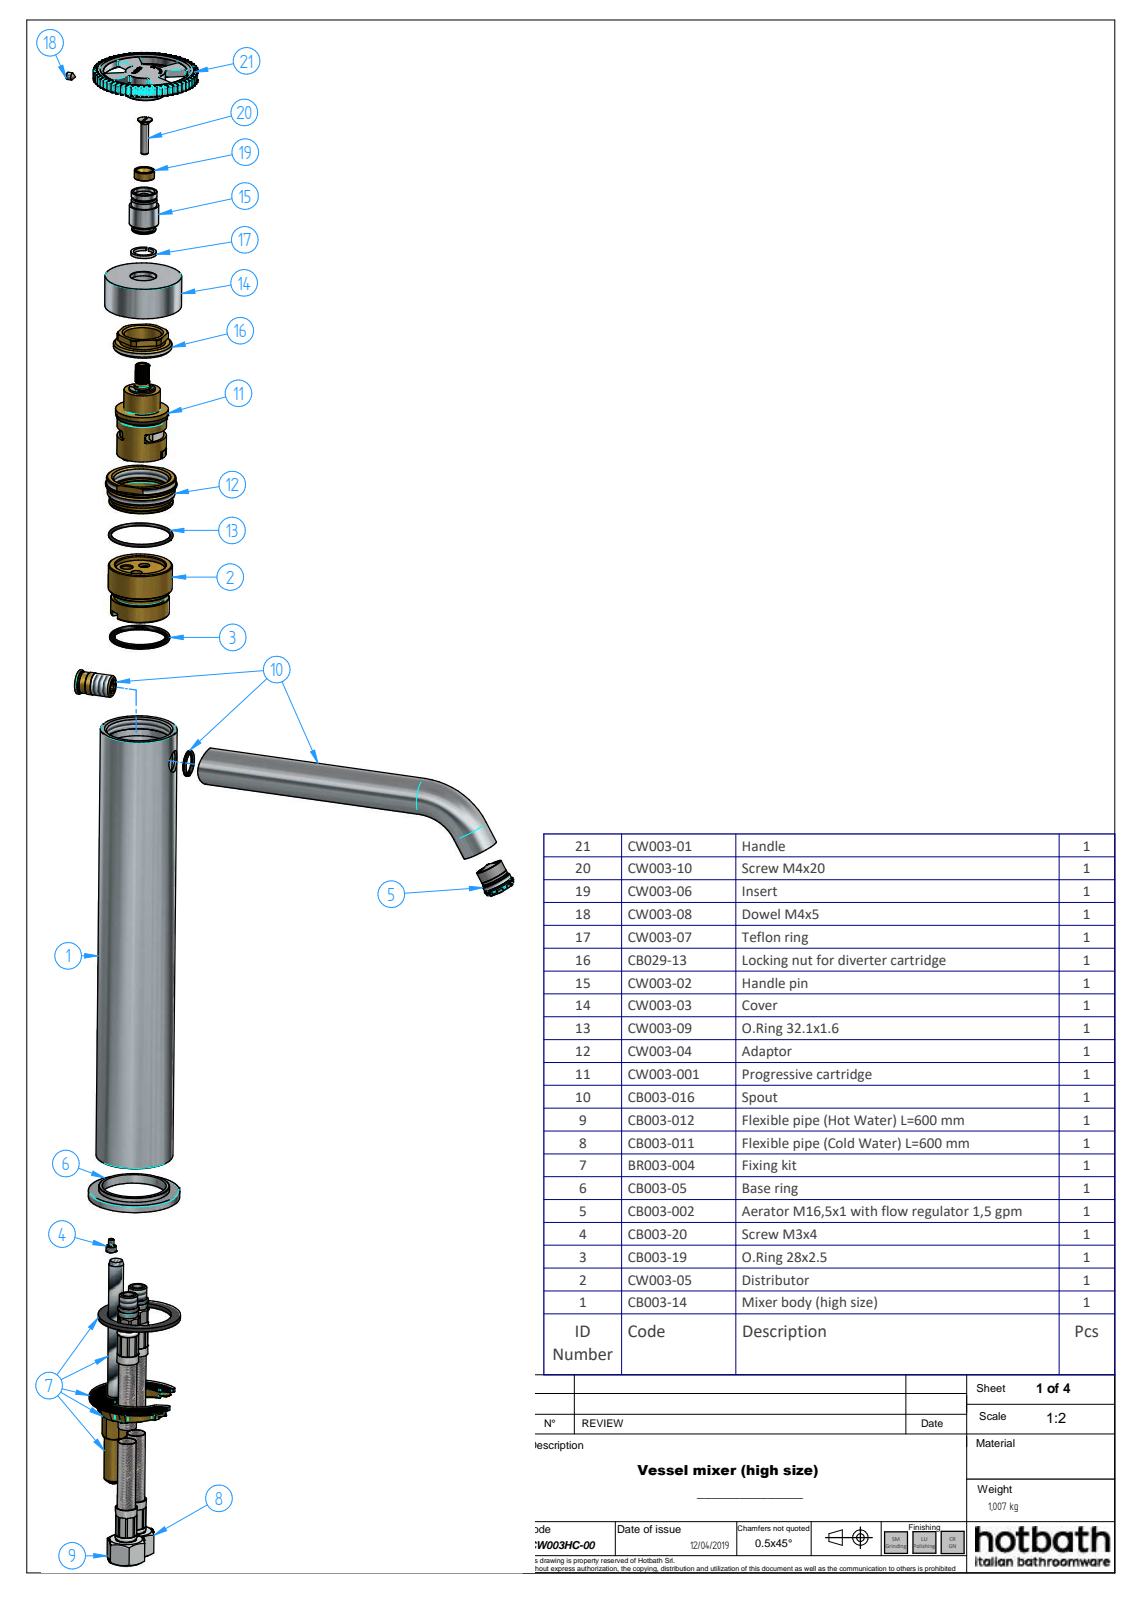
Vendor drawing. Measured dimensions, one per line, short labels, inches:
name: CW003HC-00; CB003-14; CW003-08; CB029-13 (+8 more)
written by: ST-DEVELOPER v16.7 (AUTOMOTIVE_DESIGN)
unit: in
bodies: 46 solids, 2940 faces (743 planar, 846 cylindrical, 1351 other)
size: 15.758 × 8.56 × 2.244
volume: 12.51 in³; area: 262.5 in²
holes: 5× ⌀0.236, 4× ⌀0.354, 2× ⌀0.157, 2× ⌀0.283, 2× ⌀0.351, 2× ⌀0.376, 2× ⌀0.413, 2× ⌀0.433, 2× ⌀0.589, 1× ⌀0.097, 1× ⌀0.128, 1× ⌀0.132
bosses: 2× ⌀0.787, 2× ⌀0.575, 2× ⌀0.567, 2× ⌀0.453, 2× ⌀0.433, 2× ⌀0.421, 2× ⌀0.394, 2× ⌀0.323
rounds: 118× R0.008, 112× R0.024, 112× R0.311, 28× R0.004, 20× R0.039, 16× R0.02, 10× R0.019, 4× R0.059
face distances: 0.098, 0.079, 10.478, 1.909, 0.157, 1.988, 12.565, 10.577, 11.439, 12.486
hole spacings: 0.394, 0.039, 0.236, 0.276, 0.419, 0.424, 0.459, 0.481
